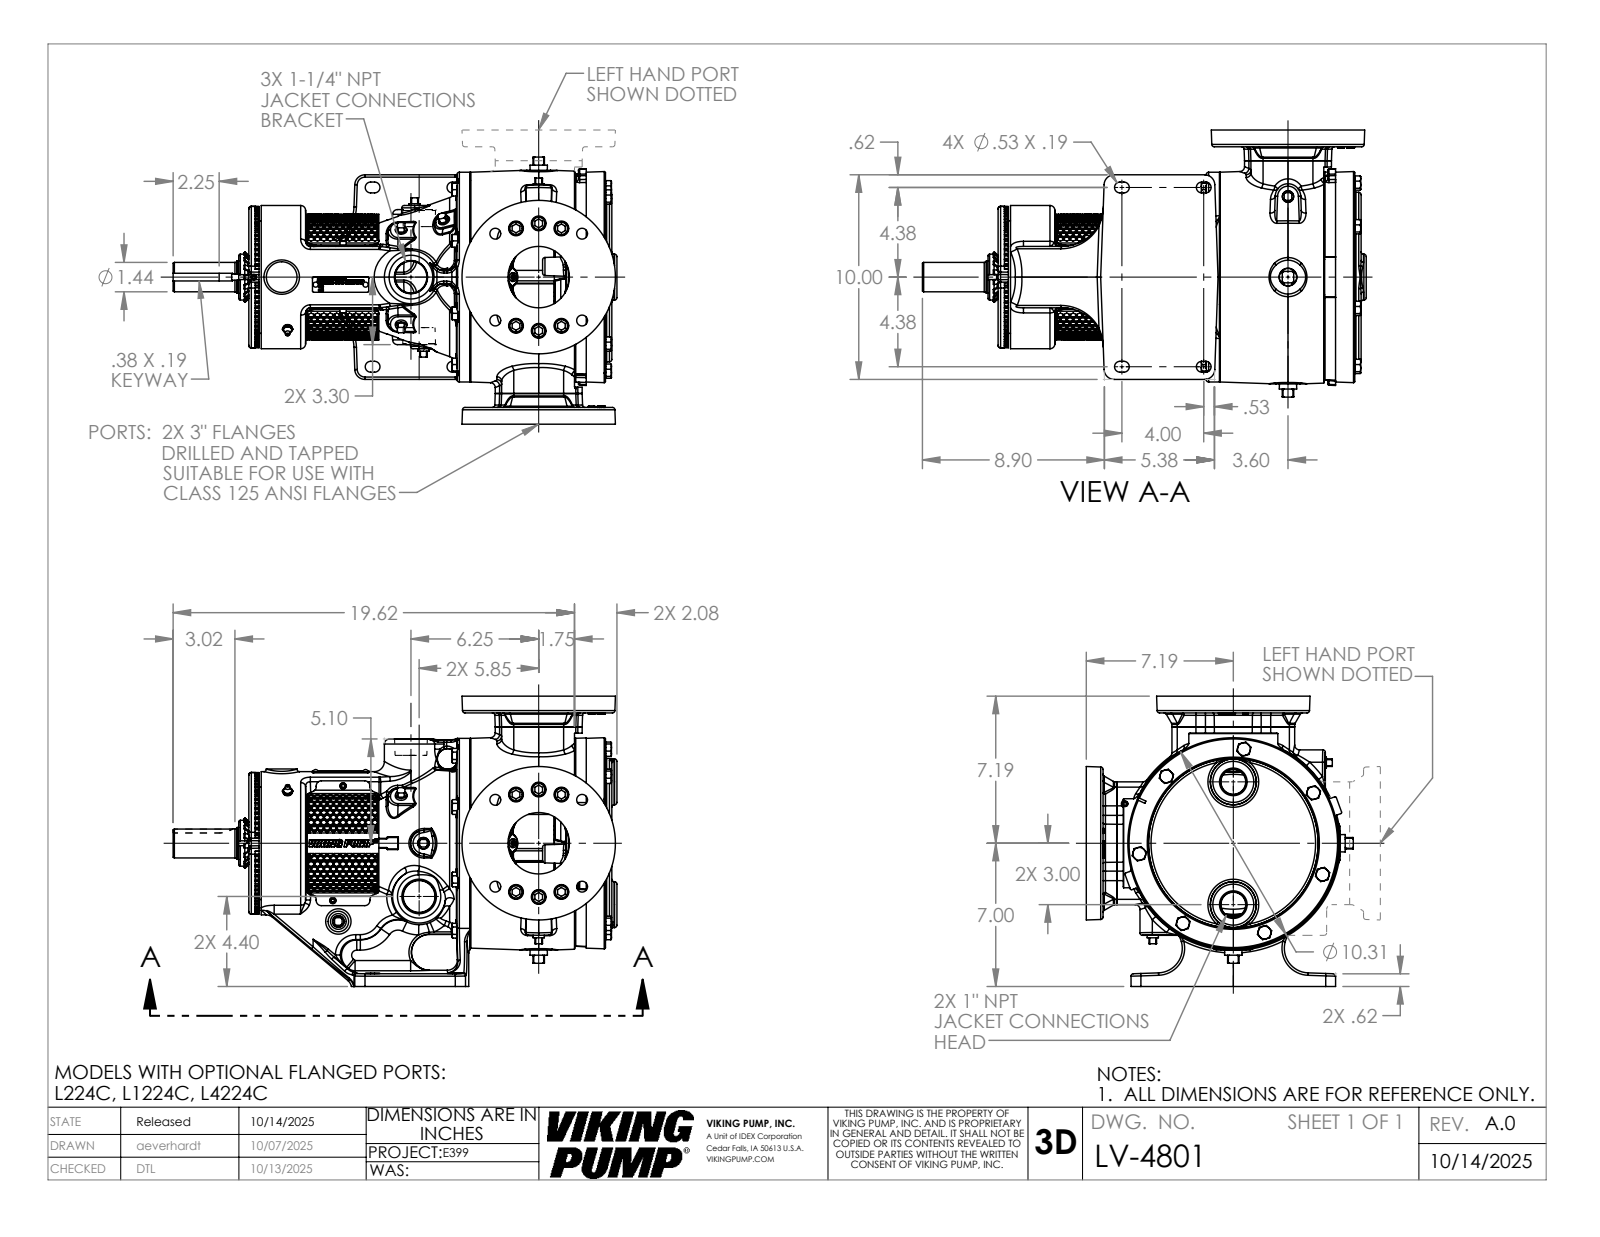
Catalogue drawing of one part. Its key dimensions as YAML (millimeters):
part_name: "LV-4801"
step_written_by: "SolidWorks 2024 (AUTOMOTIVE_DESIGN)"
units: millimeters
bodies: {solids: 1, faces: 4956, planar: 1512, cylindrical: 963, other: 2481}
overall_size: [551.1, 360.4, 331.5]
volume: 17990000
surface_area: 910300
round_holes:
  - {diameter: 11.9, count: 12}
  - {diameter: 18.3, count: 12}
  - {diameter: 6.4, count: 9}
  - {diameter: 13.5, count: 8}
  - {diameter: 27.8, count: 8}
  - {diameter: 5.1, count: 6}
  - {diameter: 4, count: 3}
  - {diameter: 6.8, count: 2}
  - {diameter: 8, count: 2}
  - {diameter: 76.2, count: 2}
  - {diameter: 11.5, count: 1}
  - {diameter: 40.1, count: 1}
round_bosses_or_shafts:
  - {diameter: 16.8, count: 12}
  - {diameter: 11.1, count: 12}
  - {diameter: 15.9, count: 9}
  - {diameter: 15.9, count: 6}
  - {diameter: 7.9, count: 3}
  - {diameter: 4.8, count: 3}
  - {diameter: 260.4, count: 1}
  - {diameter: 177.8, count: 1}
partial_cylinders:
  - {radius: 1.6, count: 109}
  - {radius: 1.8, count: 74}
  - {radius: 3, count: 62}
  - {radius: 0.3, count: 30}
  - {radius: 0.2, count: 26}
  - {radius: 12.7, count: 26}
  - {radius: 0.8, count: 18}
  - {radius: 6.1, count: 16}
face_to_face_distances: [360.3, 20.8, 7.9, 373, 380.9, 89.8, 283.2, 291.1, 57.2, 12.7]
hole_center_spacings: [76.2, 107.8, 66.7, 34.9, 26.5, 28.9, 55.4, 55.4]
